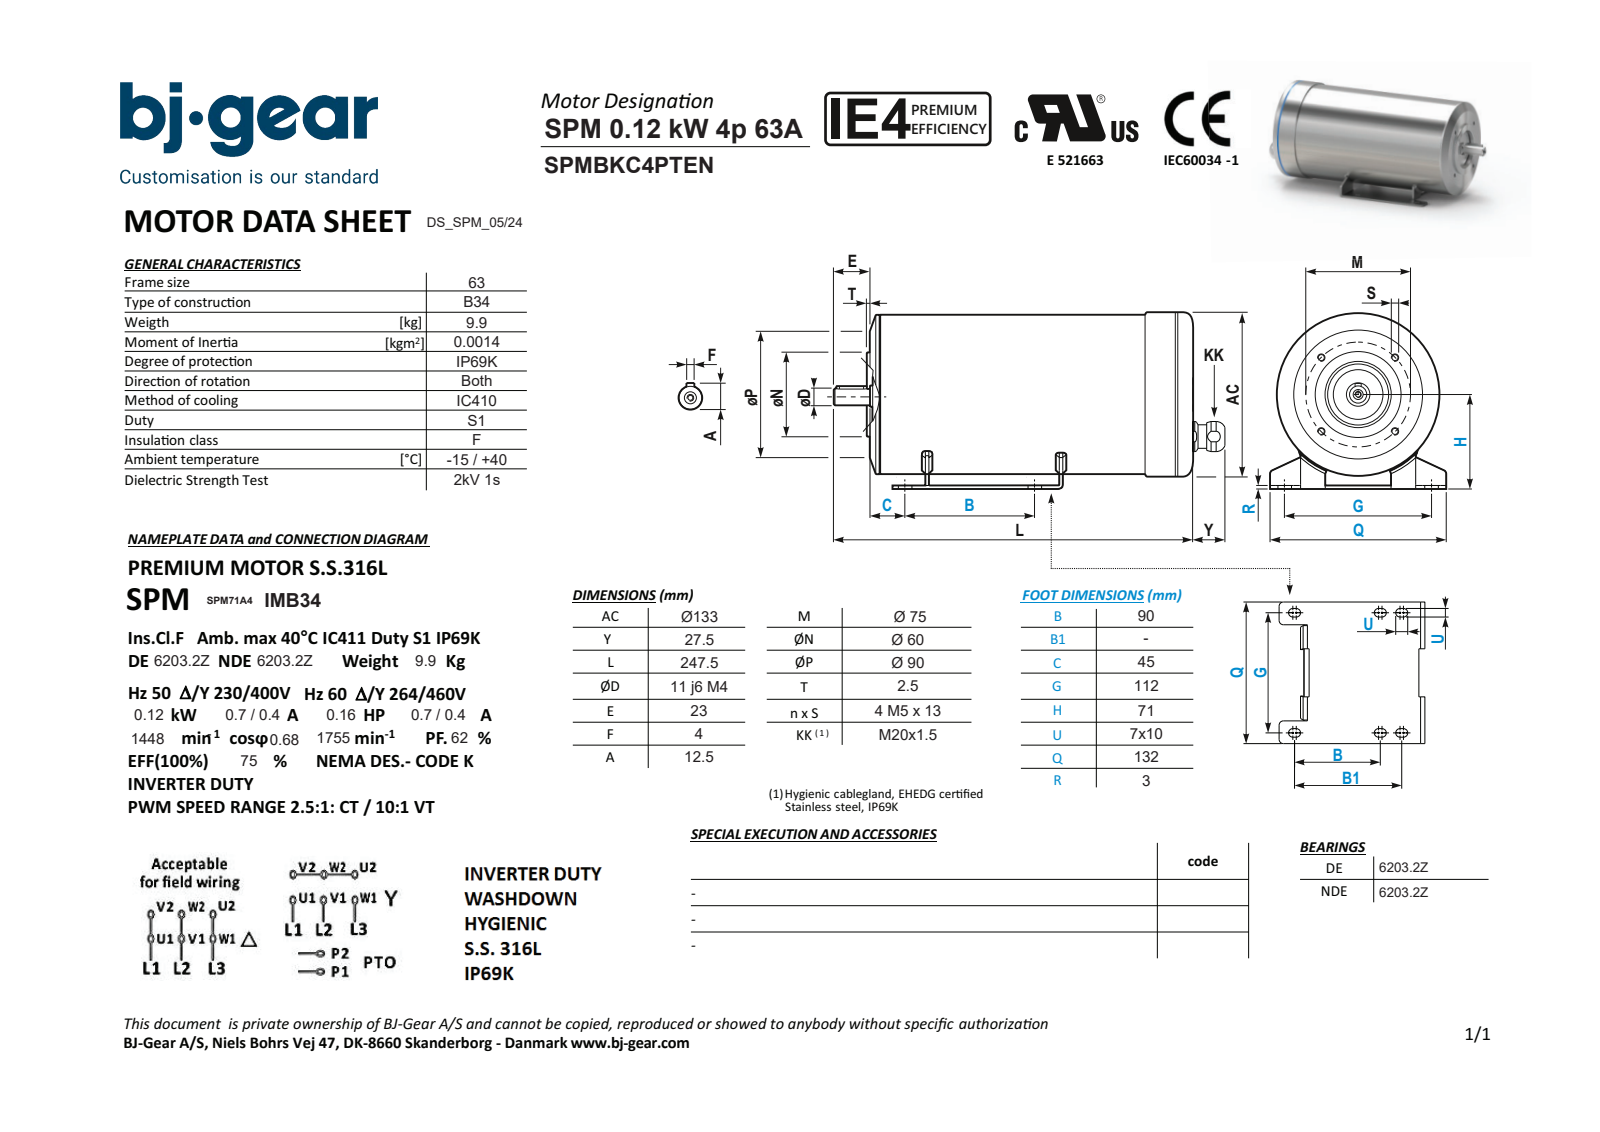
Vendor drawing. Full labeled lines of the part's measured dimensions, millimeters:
Part name (STEP PRODUCT): SPMBKD2PTENN4KSA1-N---NNN; SPMBKD2JTENN4KSA1-N---NNN; SPM719022
STEP written by: Solid Edge (AUTOMOTIVE_DESIGN)
Units: millimetres
Bodies: 2 solids, 157 faces (66 planar, 66 cylindrical, 25 other)
Overall size (bounding box): 275 × 137.5 × 133
Volume: 2 984 000 mm³ · Surface area: 153 290 mm²
Round holes (diameter × count): ⌀4.13 ×4, ⌀3.24 ×1, ⌀4.3 ×1, ⌀7 ×1, ⌀13.4 ×1, ⌀52 ×1, ⌀129 ×1
Round bosses / shafts (diameter × count): ⌀133 ×1, ⌀132.98 ×1, ⌀128.98 ×1, ⌀60 ×1, ⌀20 ×1, ⌀17 ×1, ⌀11 ×1
Partial cylindrical surfaces — rounded edges, fillets, slot ends (radius × count): R3 ×8, R3.5 ×8, R1 ×4, R5 ×4, R2 ×2, R4 ×2, R12.8 ×1
Main face-to-face distances: 3, 224.5, 219, 5.5, 148.5, 151.5, 67.5, 70.5, 157, 154
Hole centre spacings: 37.5, 53.04, 27.55, 66.08, 75.01, 34
